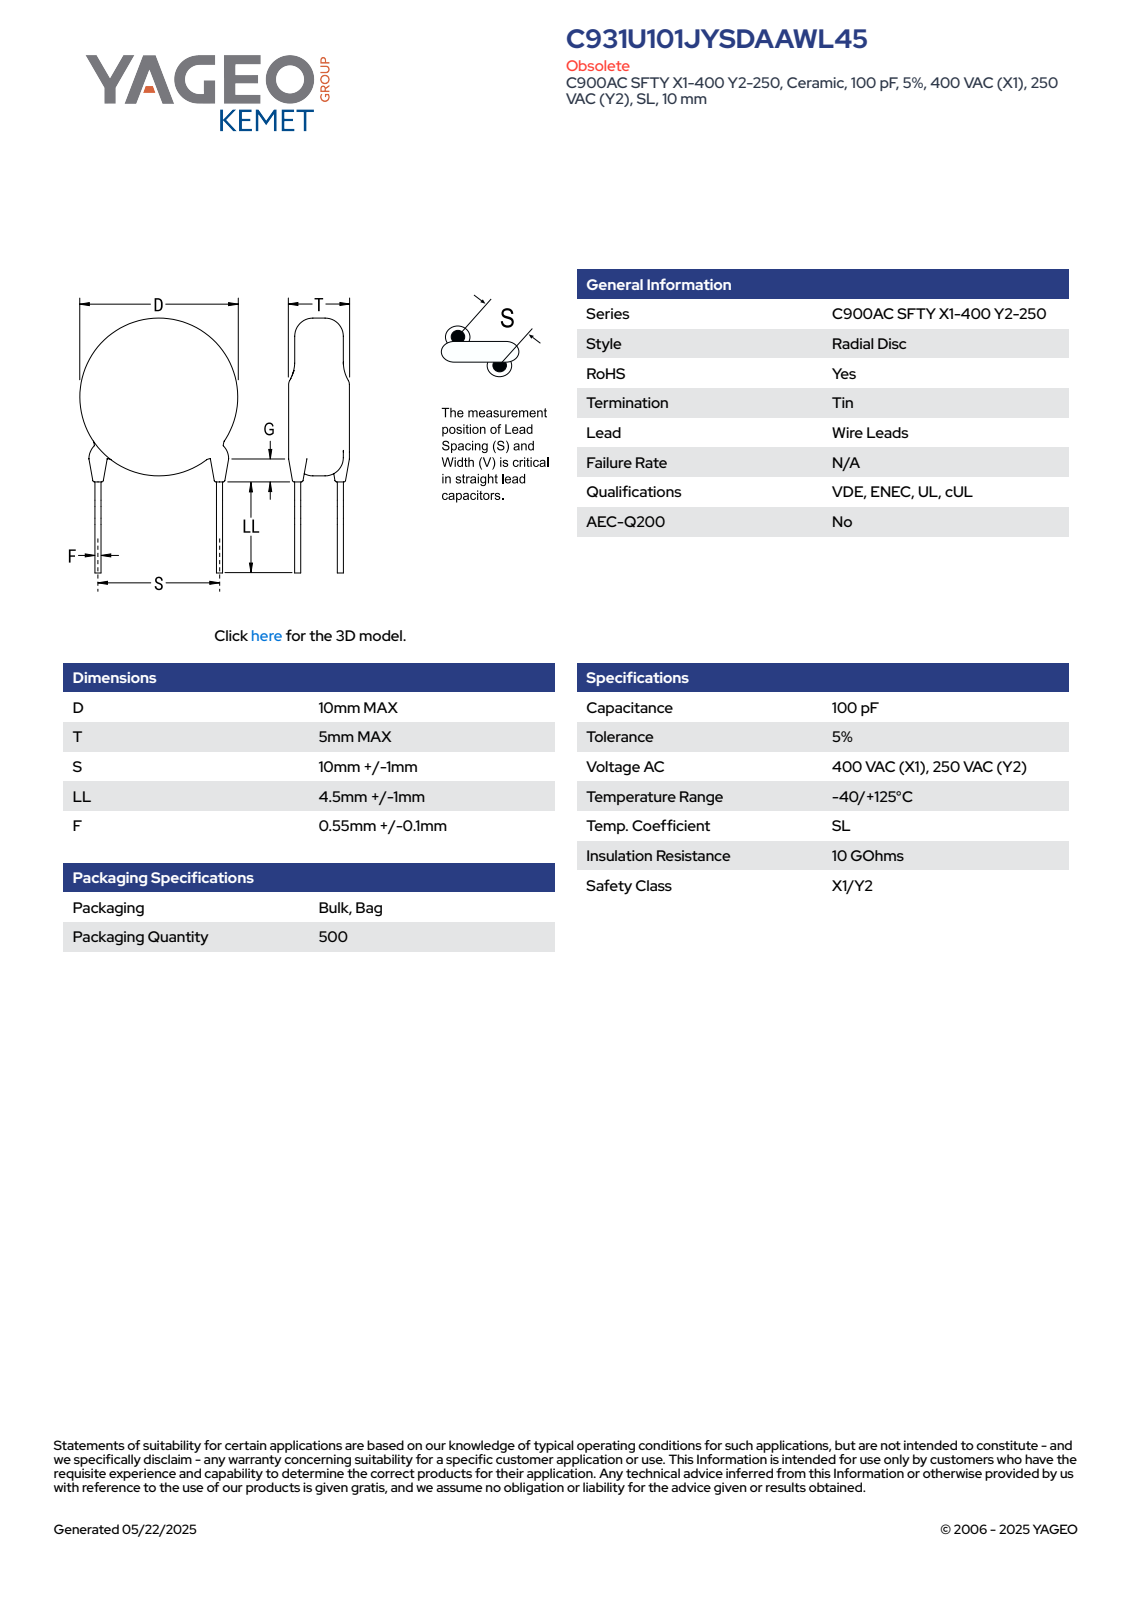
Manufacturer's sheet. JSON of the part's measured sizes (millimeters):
{"part_name": "CCD_STC900_D10T5S10LL5.5F0.65G3", "step_written_by": "SolidWorks 2014 (AUTOMOTIVE_DESIGN)", "units": "millimeters", "bodies": {"solids": 4, "faces": 83, "planar": 61, "cylindrical": 6, "other": 16}, "overall_size": [15.87, 10.41, 5], "volume_mm3": 388, "surface_area_mm2": 330, "round_bosses_or_shafts": [[0.65, 2], [10, 1]], "face_to_face_distances": [5, 11.44, 10.29, 1.15, 0.93, 0.42, 0.31, 3.43, 3.56, 1.89]}
